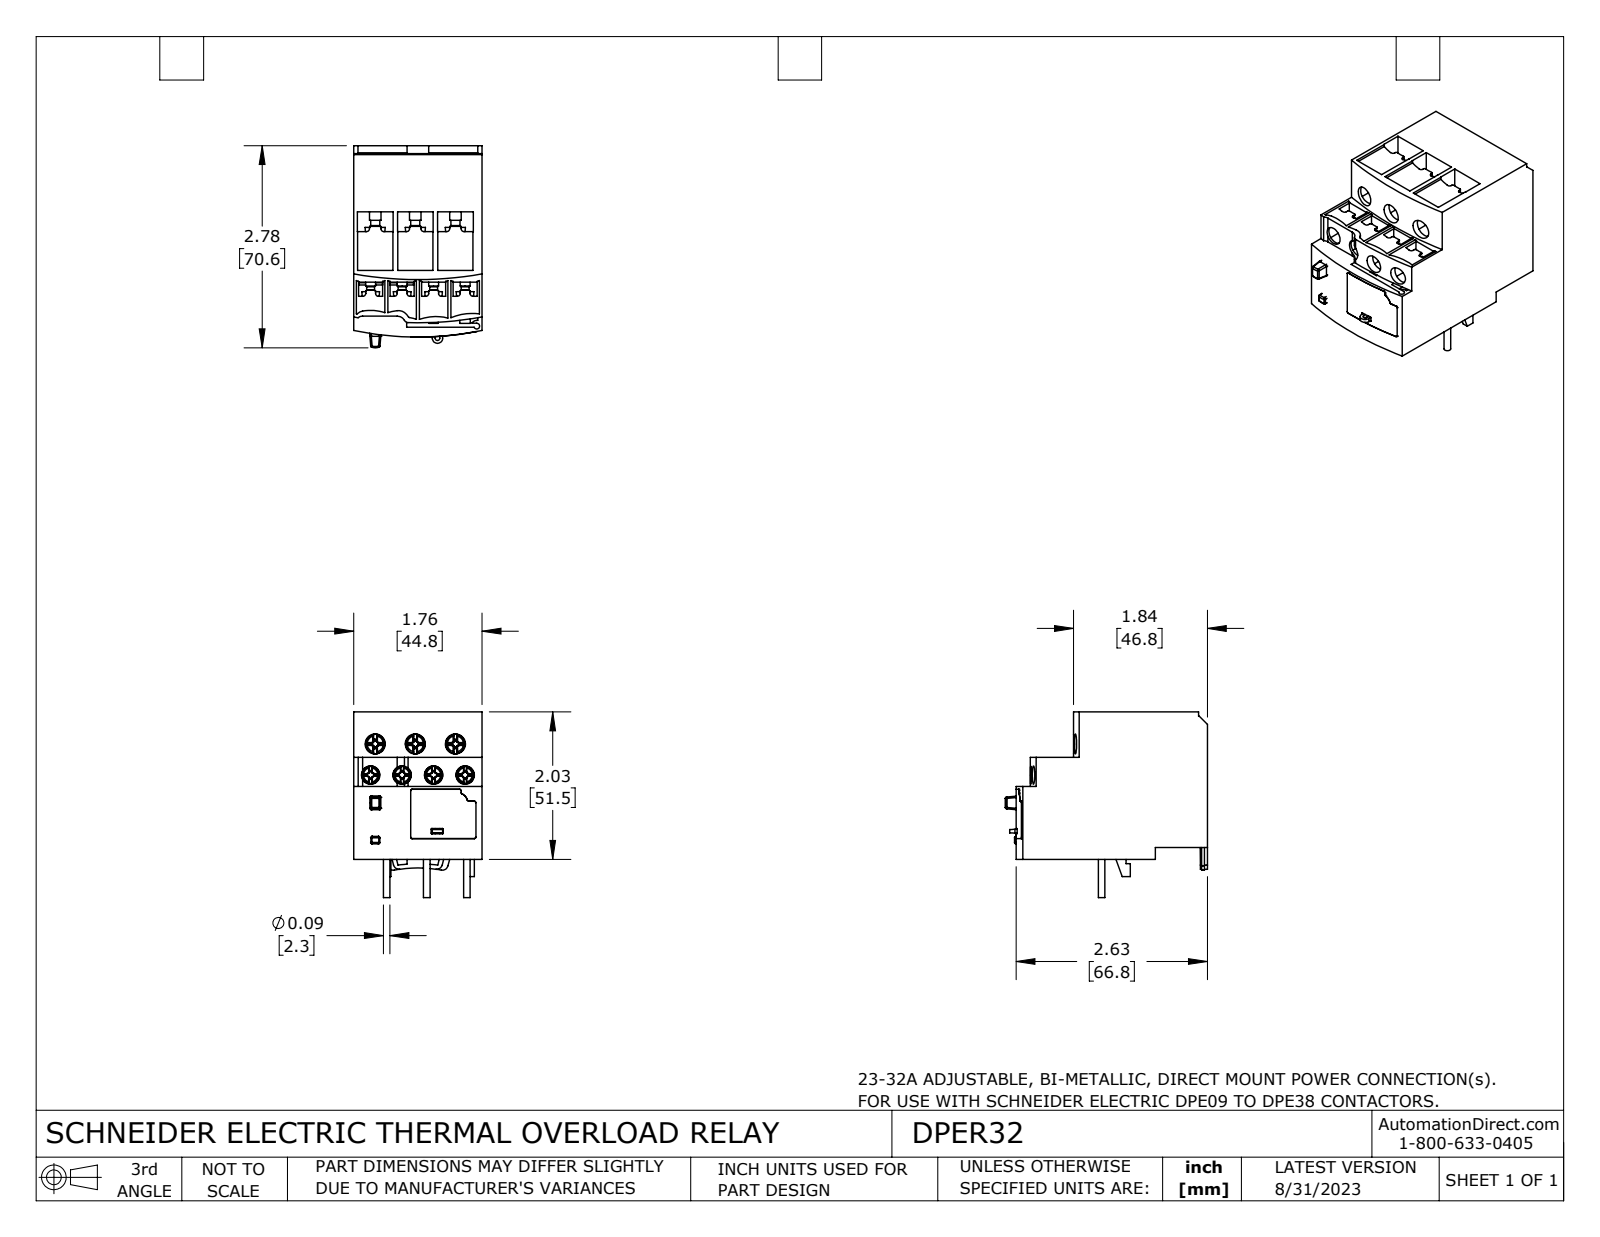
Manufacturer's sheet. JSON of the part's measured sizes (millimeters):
{"part_name": "DPER32", "step_written_by": "SolidWorks 2021 (CONFIG_CONTROL_DESIGN)", "units": "millimeters", "bodies": {"solids": 16, "faces": 1212, "planar": 676, "cylindrical": 269, "other": 267}, "overall_size": [70.6, 64.8, 44.8], "volume_mm3": 113900, "surface_area_mm2": 30420, "round_holes": [[6.4, 4], [7, 3], [2, 2], [3, 2], [1.5, 1], [6.2, 1]], "round_bosses_or_shafts": [[2.3, 12], [3.5, 4], [2.7, 4], [4, 3], [3.9, 3], [3.1, 3], [3, 1], [2.7, 1]], "partial_cylinders_radius": [[0.5, 52], [1, 22], [0.1, 19], [0.3, 8], [0.2, 6], [16, 6], [2, 4], [0.6, 2]], "face_to_face_distances": [44.8, 4.2, 51.5, 47.3, 23.1, 14, 15.7, 35.8, 31.6, 63.4], "hole_center_spacings": [11, 14, 22, 8.5, 9.7, 10.3, 10.7, 11.4]}
